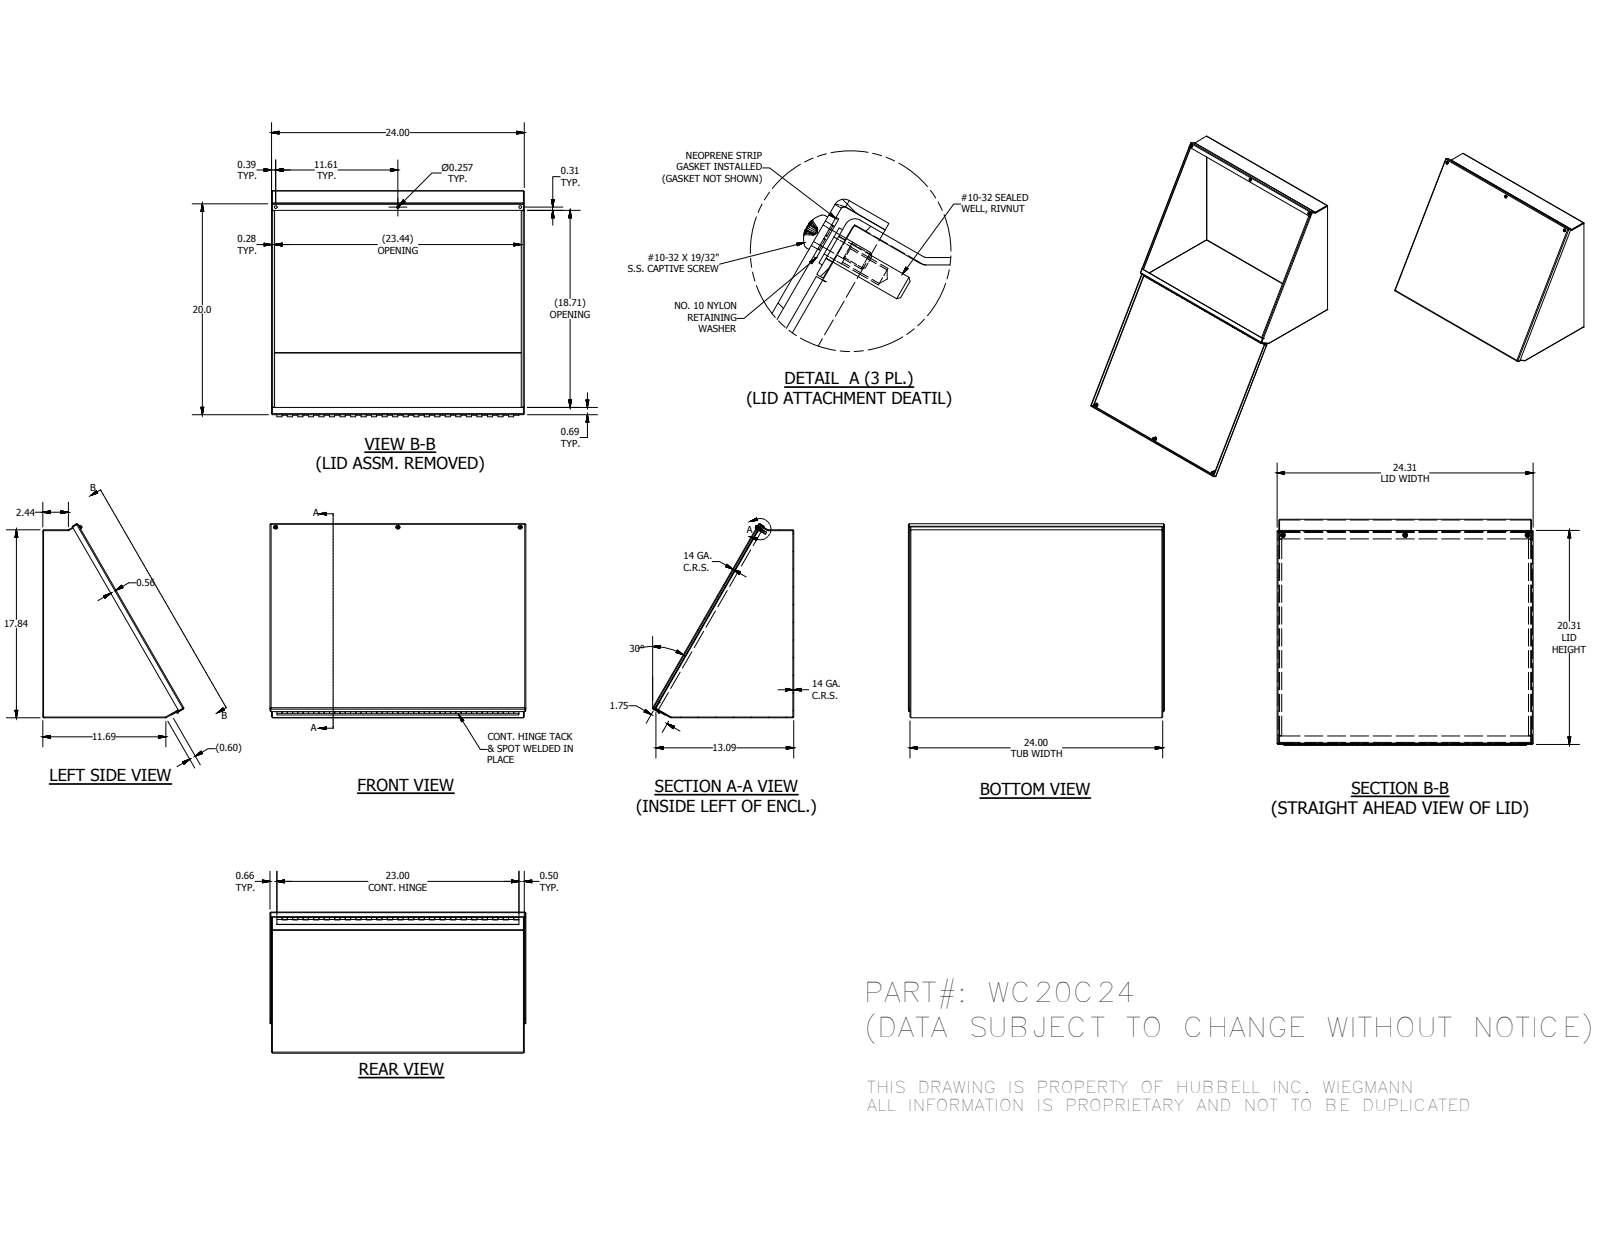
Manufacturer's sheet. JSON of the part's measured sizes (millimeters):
{"part_name": "WC20C24BTB; WC20C24LID; WC20CLS; WC20CRS (+8 more)", "step_written_by": "Autodesk Inventor 2014 (AUTOMOTIVE_DESIGN)", "units": "millimeters", "bodies": {"solids": 16, "faces": 597, "planar": 364, "cylindrical": 159, "other": 74}, "overall_size": [617.54, 468.05, 340.23], "volume_mm3": 2076000, "surface_area_mm2": 2249000, "round_holes": [[3.96, 3], [4.98, 3], [6.53, 3], [7.06, 3], [7.14, 3], [2.96, 1]], "round_bosses_or_shafts": [[11.51, 3], [10.31, 3], [9.47, 3], [6.3, 3], [4.83, 3], [5.08, 1], [2.54, 1]], "partial_cylinders_radius": [[0.79, 12], [2.67, 12], [2.27, 3]], "face_to_face_distances": [1.88, 607.72, 605.84, 609.6, 451.35, 449.47, 453.23, 2.94, 3.97, 611.69], "hole_center_spacings": [294.97, 589.94, 1.31]}
